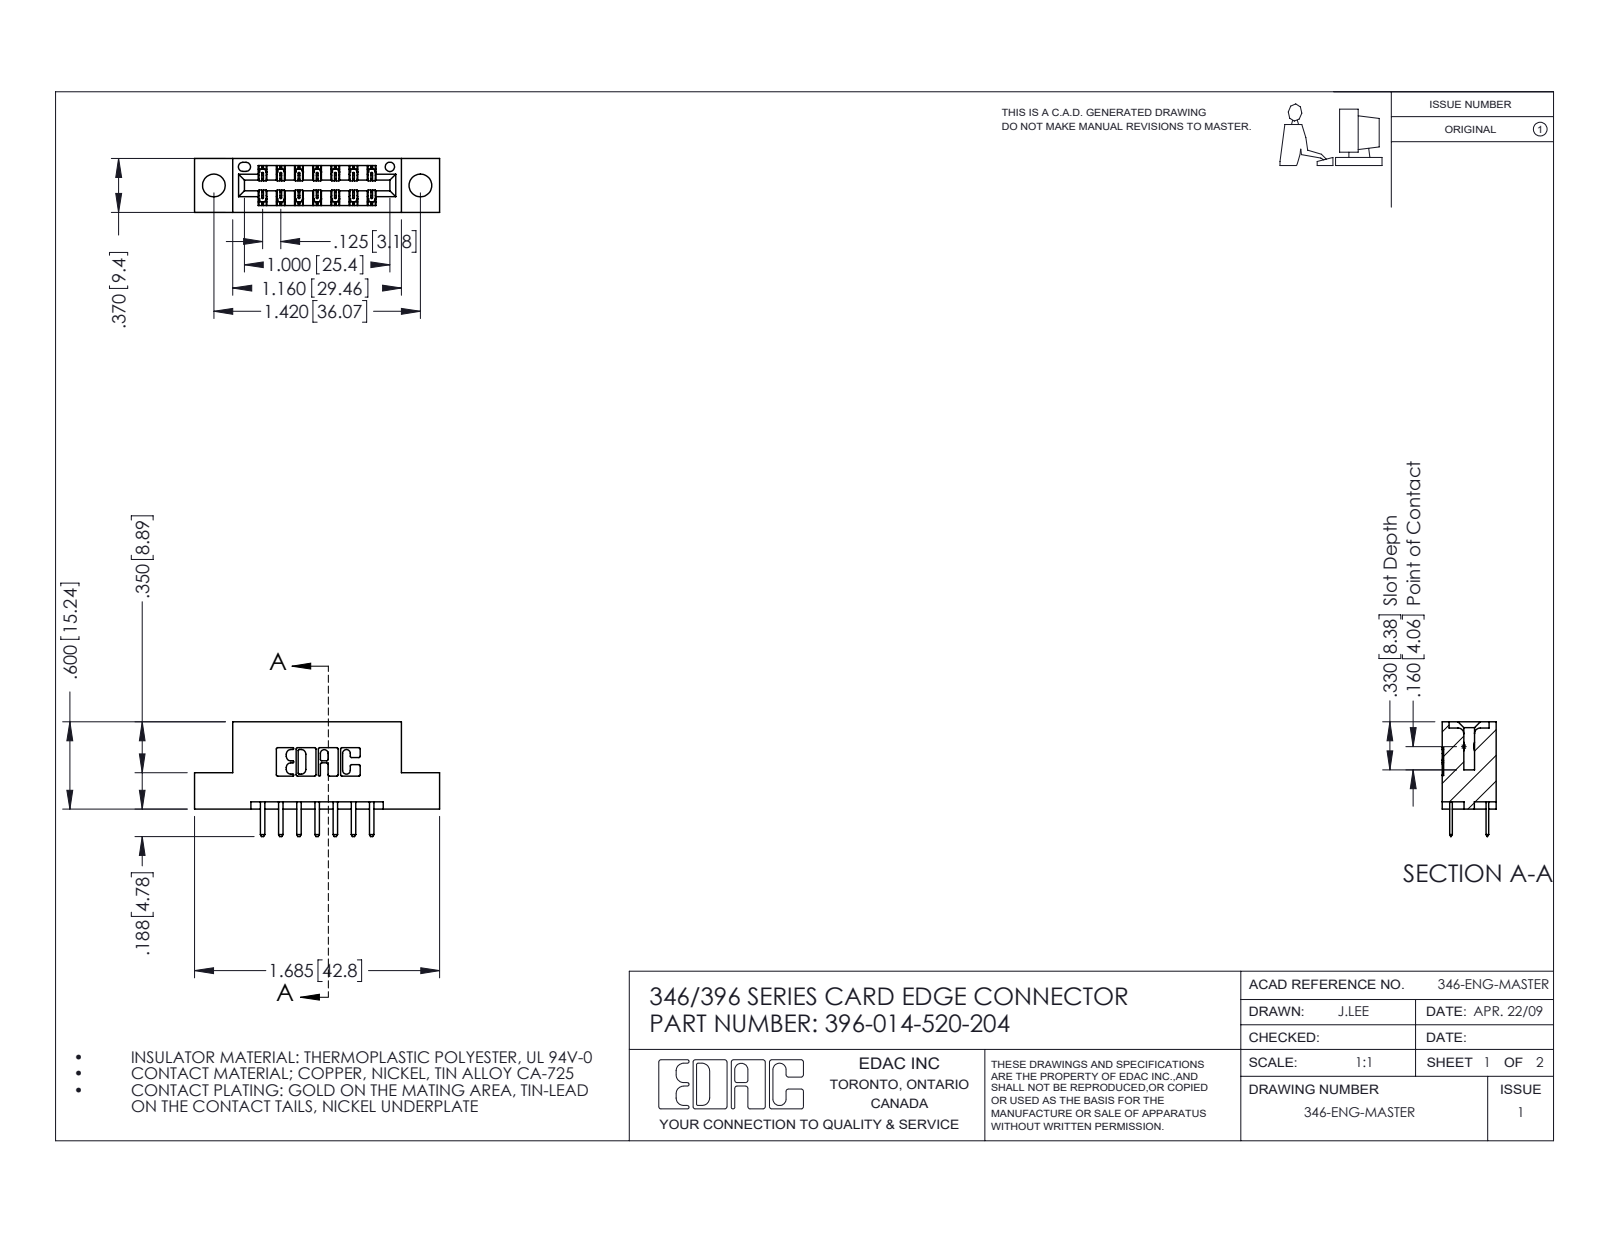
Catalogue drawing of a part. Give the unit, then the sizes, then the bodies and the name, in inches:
Units: inches
Overall size (bounding box): 1.685 × 0.788 × 0.37
Round holes (diameter × count): ⌀0.156 ×2, ⌀0.064 ×1
Partial cylindrical surfaces — rounded edges, fillets, slot ends (radius × count): R0.01 ×22, R0.006 ×21, R0.01 ×18, R0.007 ×6, R0.031 ×6, R0.026 ×3, R0.014 ×2, R0.022 ×2
Main face-to-face distances: 0.25, 0.37, 0.048, 0.322, 0.148, 0.222, 0.1, 0.174, 0.125, 0.185
Hole centre spacings: 0.246, 1.217, 1.42
Volume: 0.232 in³ · Surface area: 6.948 in²
Bodies: 15 solids, 906 faces (594 planar, 312 cylindrical, 0 other)
Part name (STEP PRODUCT): 345-292-001_345-293-120; 346 Part_Flush Mounting Lugs - 0.156 Dia-TH; 396-014-520-204
STEP written by: SolidWorks 2016 (CONFIG_CONTROL_DESIGN)
